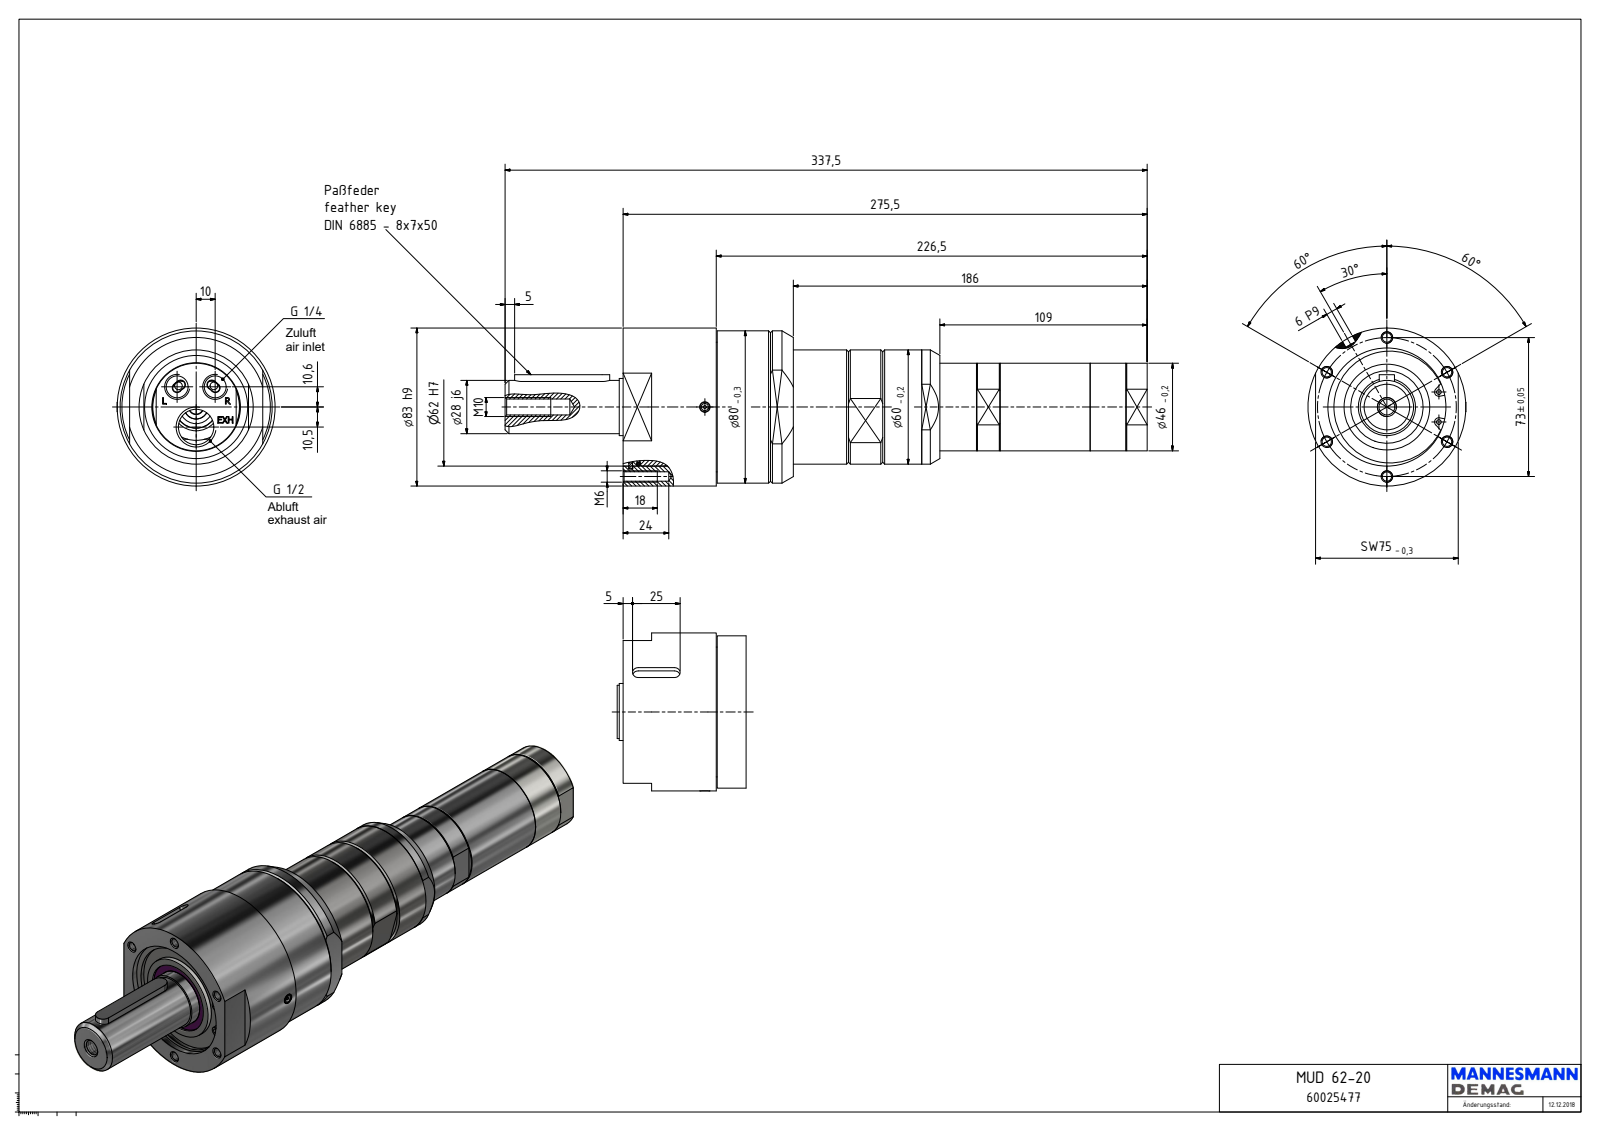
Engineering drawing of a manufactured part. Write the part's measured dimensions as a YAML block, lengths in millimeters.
part_name: "MUD 62-20_60025477"
step_written_by: "Autodesk Inventor 2018 (AUTOMOTIVE_DESIGN)"
units: millimeters
bodies: {solids: 1, faces: 584, planar: 234, cylindrical: 279, other: 71}
overall_size: [337.5, 83, 83]
volume: 872523
surface_area: 89592
round_holes:
  - {diameter: 4.92, count: 6}
  - {diameter: 1.55, count: 3}
  - {diameter: 2.5, count: 2}
  - {diameter: 4, count: 2}
  - {diameter: 5.5, count: 2}
  - {diameter: 11.45, count: 2}
  - {diameter: 8.38, count: 1}
  - {diameter: 18.63, count: 1}
  - {diameter: 36.5, count: 1}
  - {diameter: 38, count: 1}
  - {diameter: 40, count: 1}
  - {diameter: 46.5, count: 1}
round_bosses_or_shafts:
  - {diameter: 5, count: 2}
  - {diameter: 3.6, count: 2}
  - {diameter: 3.3, count: 2}
  - {diameter: 83, count: 1}
  - {diameter: 80, count: 1}
  - {diameter: 68.18, count: 1}
  - {diameter: 60, count: 1}
  - {diameter: 46, count: 1}
partial_cylinders:
  - {radius: 3.5, count: 94}
  - {radius: 6.47, count: 4}
  - {radius: 2.25, count: 2}
  - {radius: 3, count: 2}
  - {radius: 4, count: 2}
  - {radius: 5, count: 2}
  - {radius: 7.69, count: 2}
  - {radius: 17.1, count: 1}
face_to_face_distances: [0.5, 49, 2.5, 5, 44, 89.5, 84.5, 40.5, 49.5, 44.5]
hole_center_spacings: [36.5, 63.22, 73, 11.21, 14.57, 22.92, 23.35, 26.48]
